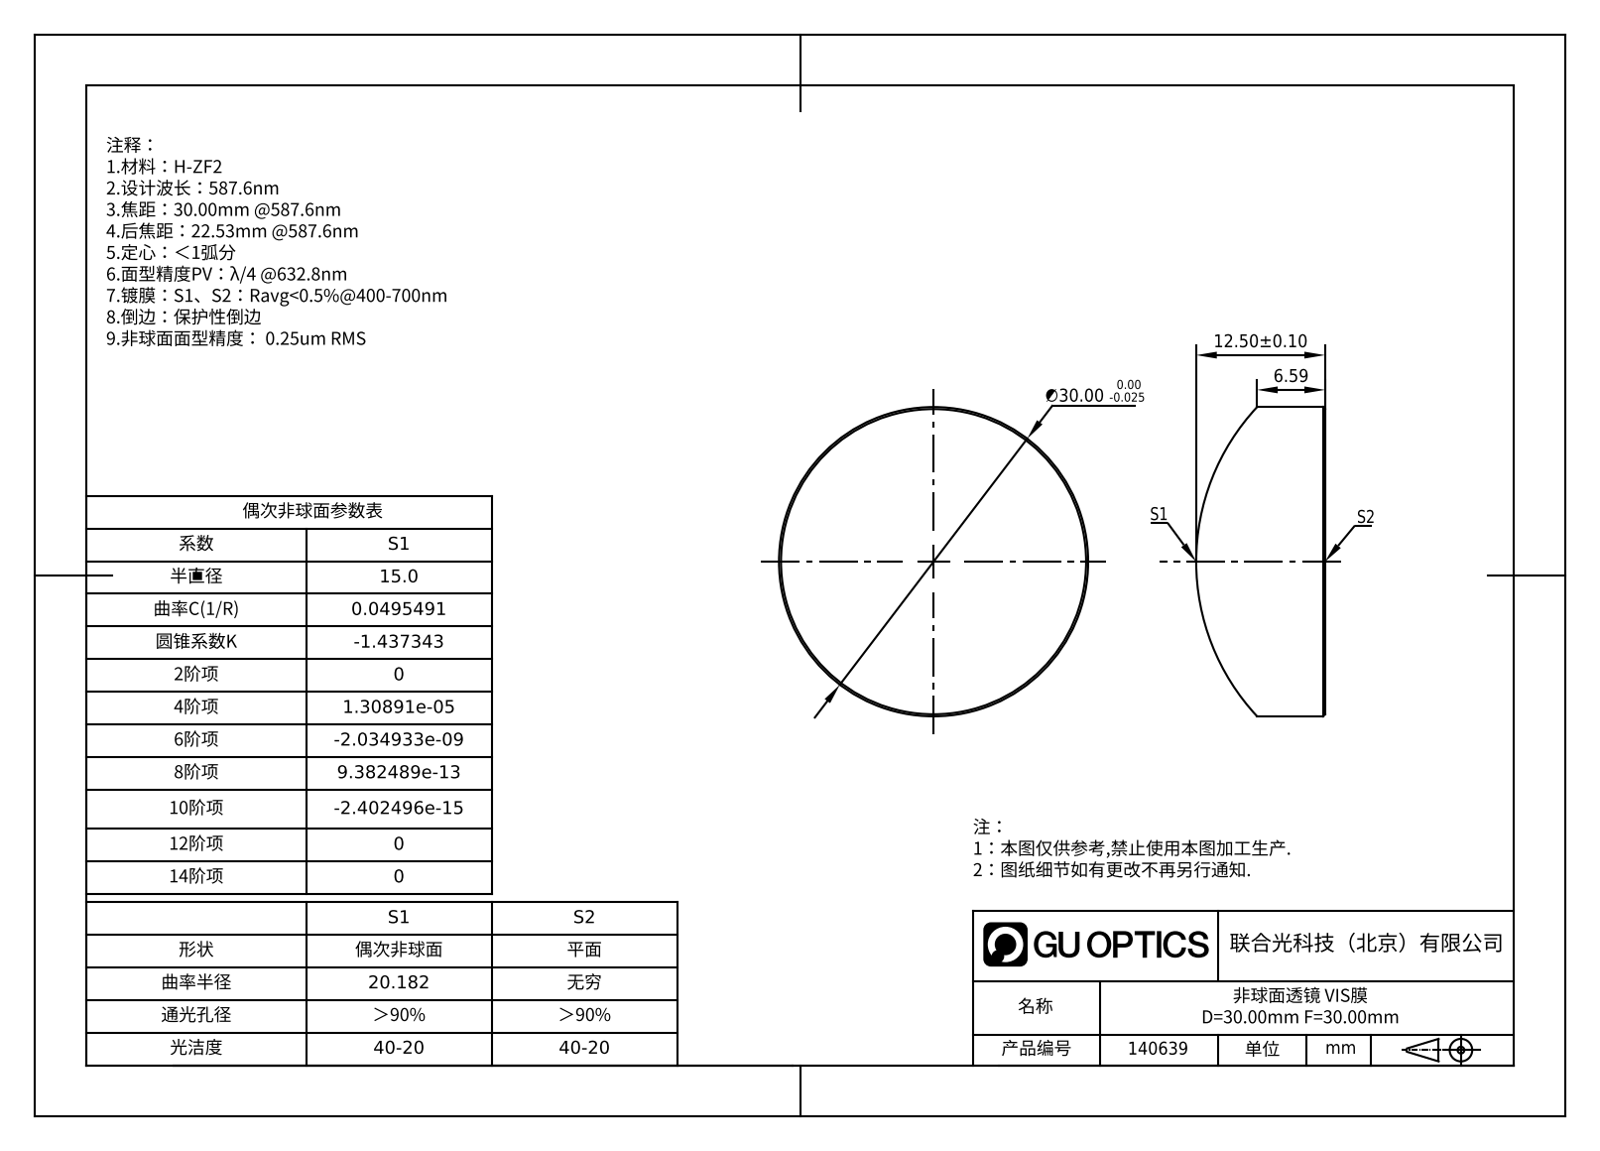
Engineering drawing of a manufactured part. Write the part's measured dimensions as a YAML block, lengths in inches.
part_name: "GLA11-030-030-H-VIS"
step_written_by: "SolidWorks 2022 (AUTOMOTIVE_DESIGN)"
units: inches
bodies: {solids: 1, faces: 7, planar: 1, cylindrical: 2, other: 4}
overall_size: [1.181, 1.181, 0.492]
volume: 0.418
surface_area: 3.306
round_bosses_or_shafts:
  - {diameter: 1.181, count: 1}
